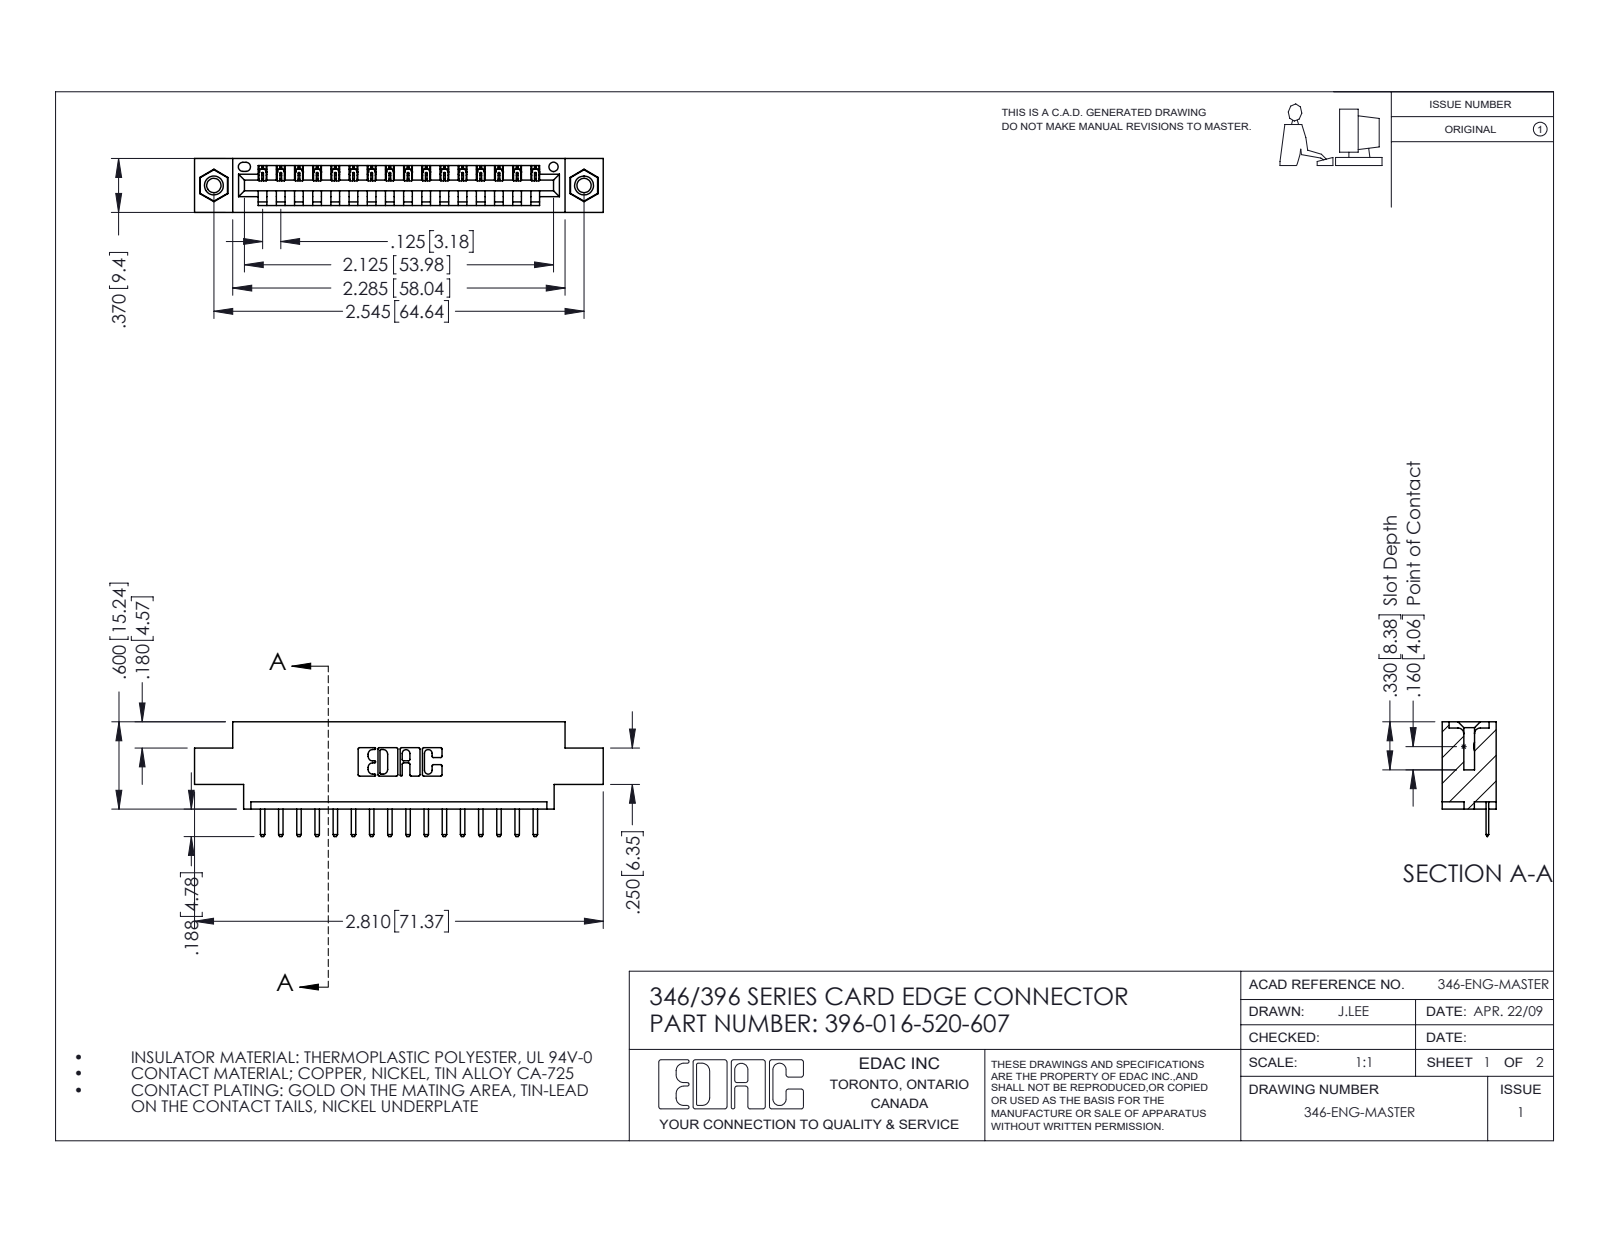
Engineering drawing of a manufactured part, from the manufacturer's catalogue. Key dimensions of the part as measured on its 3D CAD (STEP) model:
Part name (STEP PRODUCT): 345-250-001_345-250-005-103; 345-292-001_345-293-120; 346 Part_0.170 Offset - 0.156 Dia-TI; 396-016-520-607
STEP written by: SolidWorks 2016 (CONFIG_CONTROL_DESIGN)
Units: inches
Bodies: 19 solids, 1178 faces (784 planar, 378 cylindrical, 16 other)
Overall size (bounding box): 2.81 × 0.788 × 0.37
Volume: 0.393 in³ · Surface area: 12.1 in²
Round holes (diameter × count): ⌀0.098 ×2, ⌀0.125 ×2, ⌀0.156 ×2, ⌀0.064 ×1
Round bosses / shafts (diameter × count): ⌀0.155 ×2
Partial cylindrical surfaces — rounded edges, fillets, slot ends (radius × count): R0.01 ×34, R0.006 ×32, R0.01 ×22, R0.007 ×6, R0.031 ×6, R0.026 ×3, R0.031 ×2, R0.04 ×2
Main face-to-face distances: 0.37, 0.048, 0.322, 0.25, 0.222, 0.148, 0.1, 0.174, 0.072, 0.298
Hole centre spacings: 0.246, 2.338, 2.545
